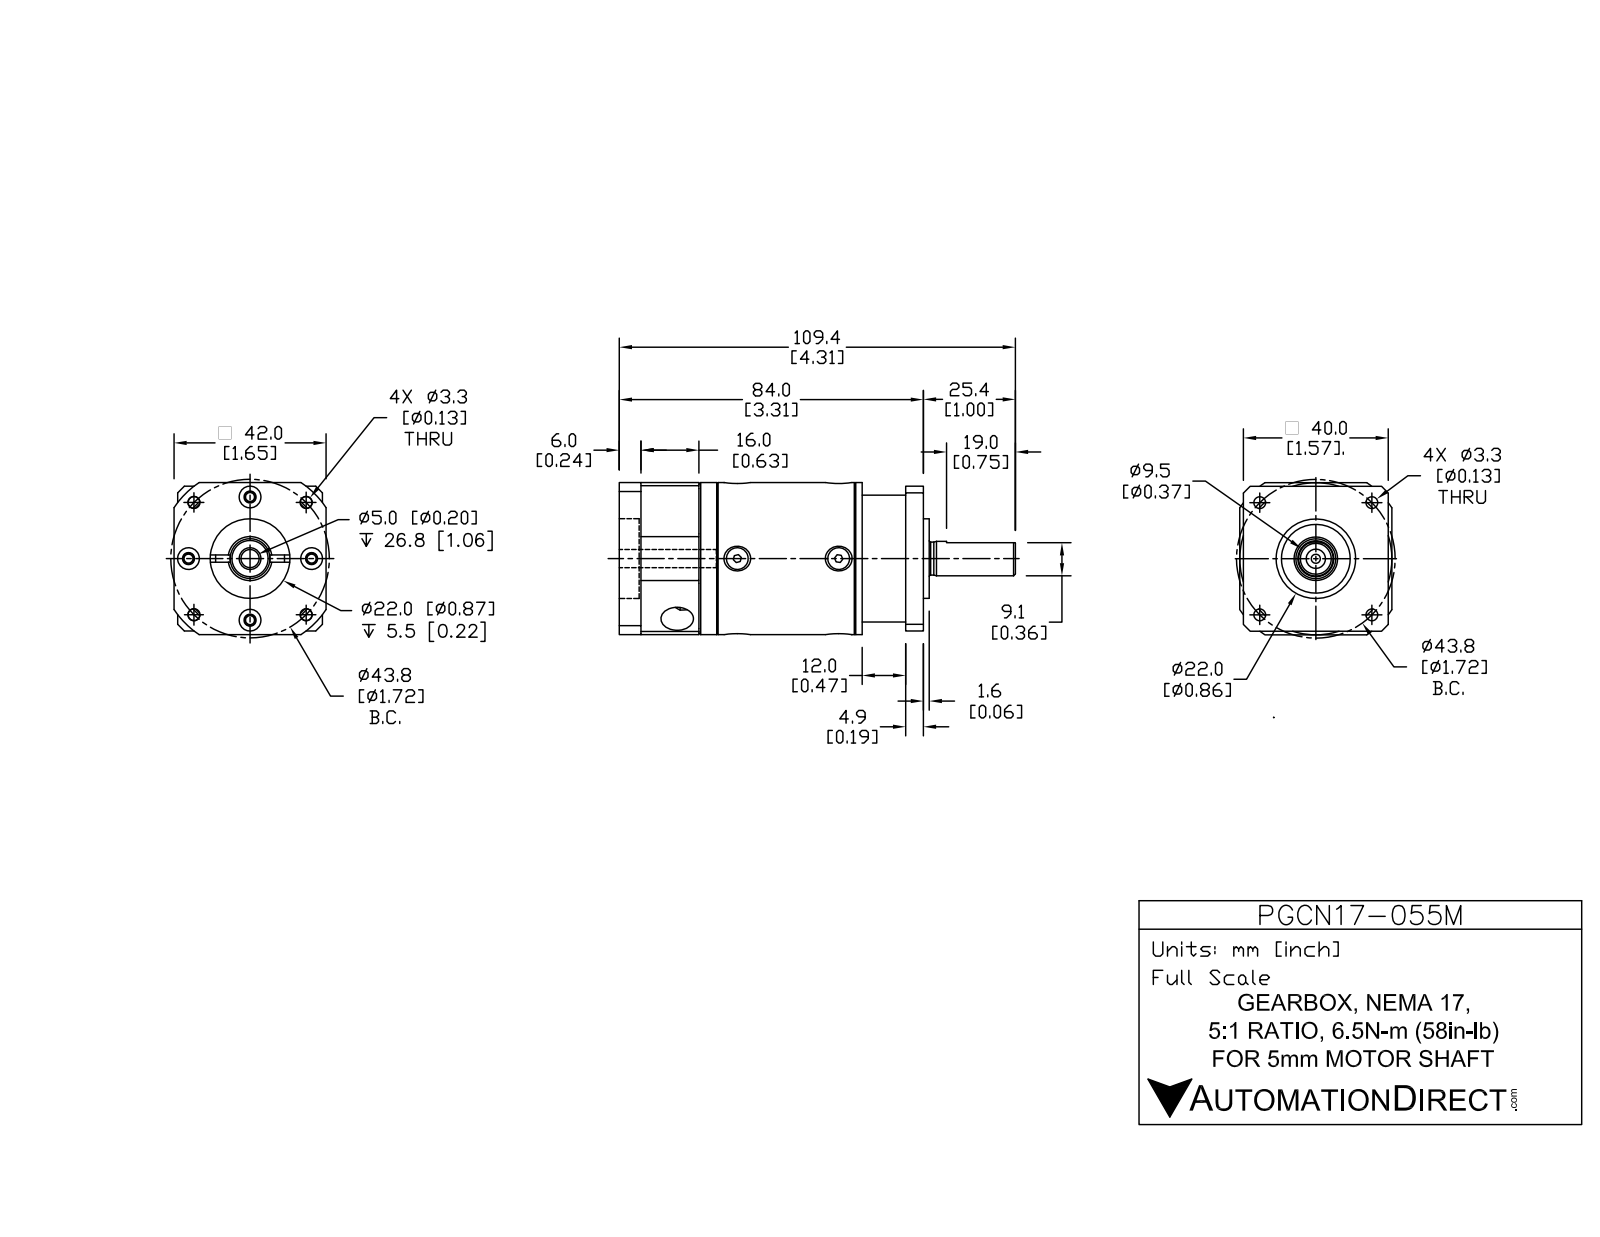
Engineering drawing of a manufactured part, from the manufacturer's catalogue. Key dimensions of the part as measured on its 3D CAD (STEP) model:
Part name (STEP PRODUCT): PGCN17-055M; PE-N17-I 11mm Input_1; Bushing_5x11x14.9_1; N17-E05_1
STEP written by: SolidWorks 2014 (AUTOMOTIVE_DESIGN)
Units: inches
Bodies: 3 solids, 433 faces (137 planar, 174 cylindrical, 122 other)
Overall size (bounding box): 4.307 × 1.654 × 1.654
Volume: 6.197 in³ · Surface area: 41.83 in²
Round holes (diameter × count): ⌀0.13 ×8, ⌀0.098 ×5, ⌀0.118 ×4, ⌀0.128 ×4, ⌀0.134 ×4, ⌀0.236 ×4, ⌀0.177 ×2, ⌀0.354 ×2, ⌀0.197 ×1, ⌀0.433 ×1, ⌀0.748 ×1, ⌀0.866 ×1
Round bosses / shafts (diameter × count): ⌀0.236 ×4, ⌀0.276 ×2, ⌀0.157 ×2, ⌀1.654 ×1, ⌀1.378 ×1, ⌀0.865 ×1, ⌀0.472 ×1, ⌀0.375 ×1
Partial cylindrical surfaces — rounded edges, fillets, slot ends (radius × count): R0.064 ×2, R0.157 ×2, R0.748 ×1, R0.995 ×1, R1.063 ×1
Main face-to-face distances: 0.866, 2.441, 3.307, 0.039, 1.614, 0.193, 2.248, 3.114, 1.457, 0.472
Hole centre spacings: 0.613, 0.613, 1.22, 1.417, 1.418, 0.669, 0.863, 0.863
